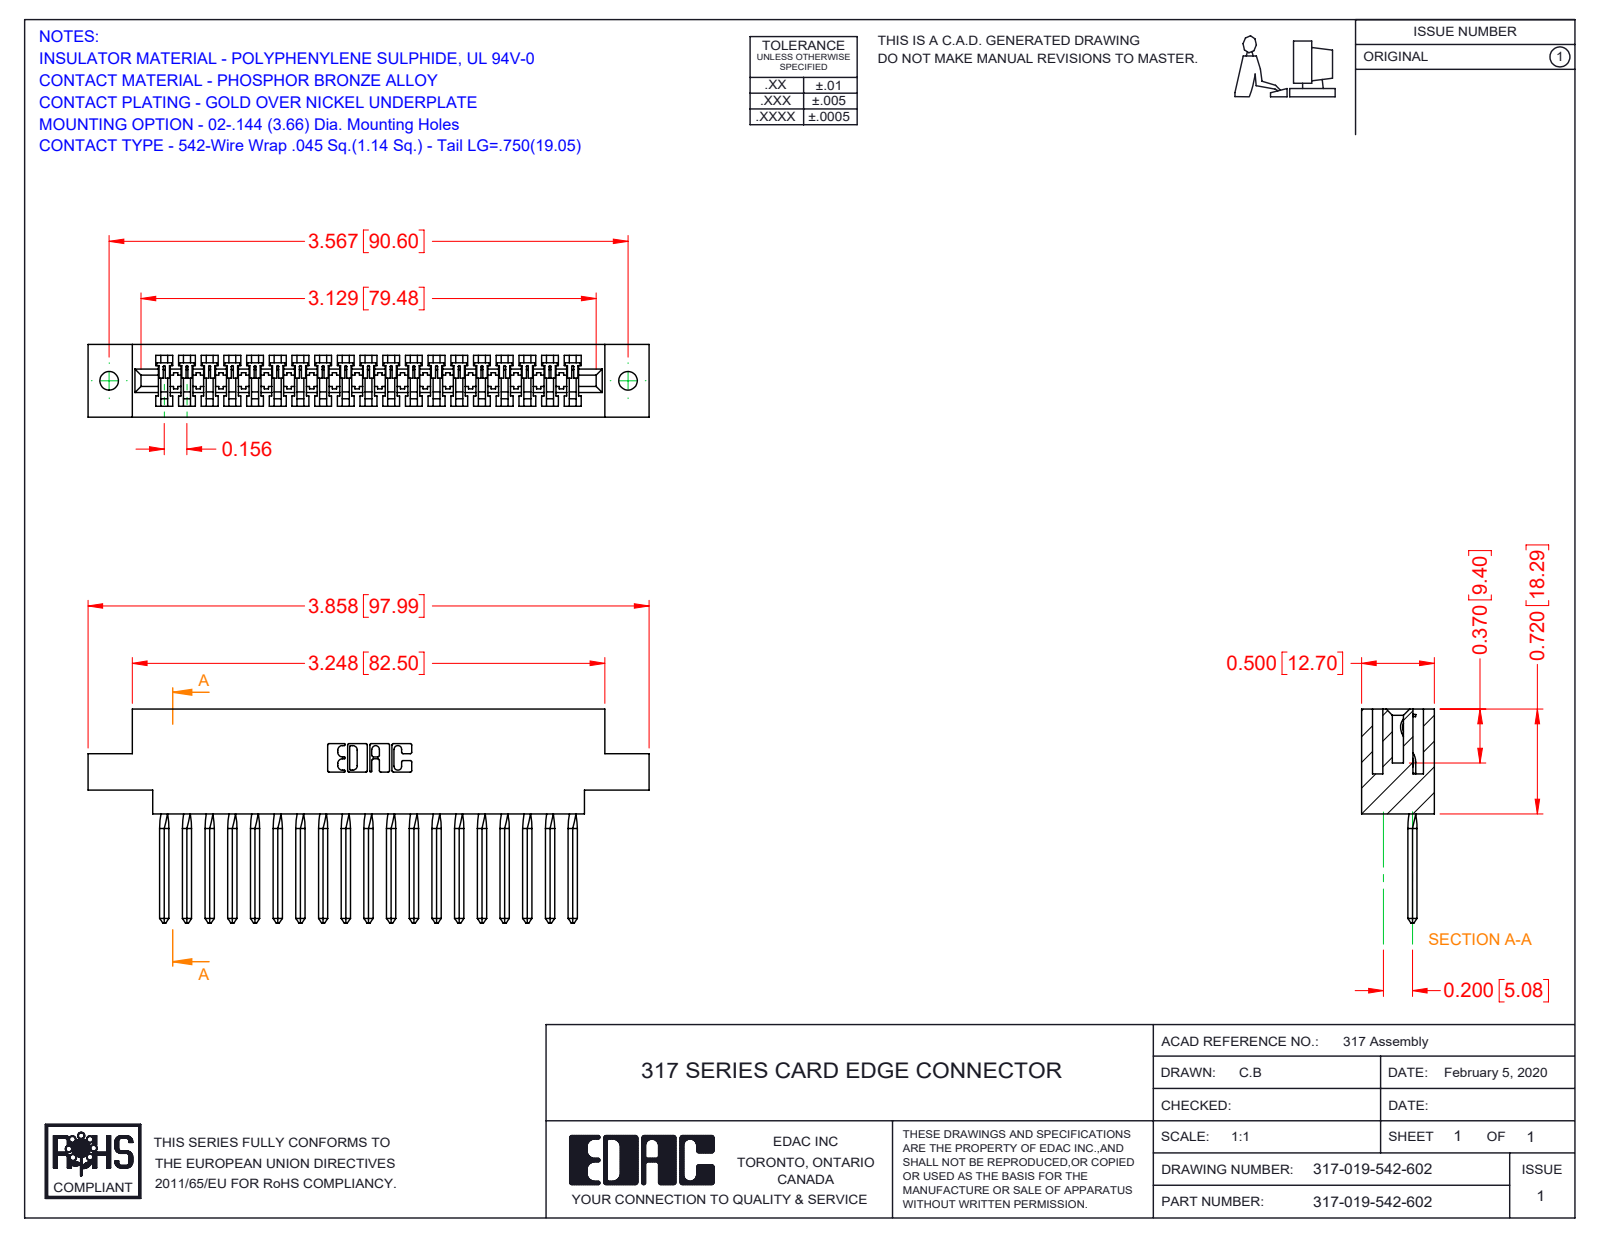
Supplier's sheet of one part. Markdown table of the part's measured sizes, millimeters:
| quantity | value |
| --- | --- |
| part name | 317-019-542-602; 317-290-003_542; 317 Part_.144 Dia |
| STEP written by | SolidWorks 2016 (CONFIG_CONTROL_DESIGN) |
| units | millimeters |
| bodies | 20 solids, 1527 faces (1274 planar, 177 cylindrical, 76 other) |
| overall size | 98 × 37.3 × 12.7 |
| volume | 14 500 mm³ |
| surface area | 16 890 mm² |
| round holes (diameter × count) | 3.3 × 2 |
| partial cylindrical surfaces (radius × count) | 0.2 × 38, 0.3 × 22, 0.2 × 6, 0.8 × 6, 0.7 × 3, 1.9 × 1, 2.3 × 1, 2.5 × 1 |
| main face-to-face distances | 12.7, 1.9, 10.8, 8.9, 2.8, 3.5, 18.3, 7.1, 5.4, 7.3 |
| hole center spacings | 90.6 |
